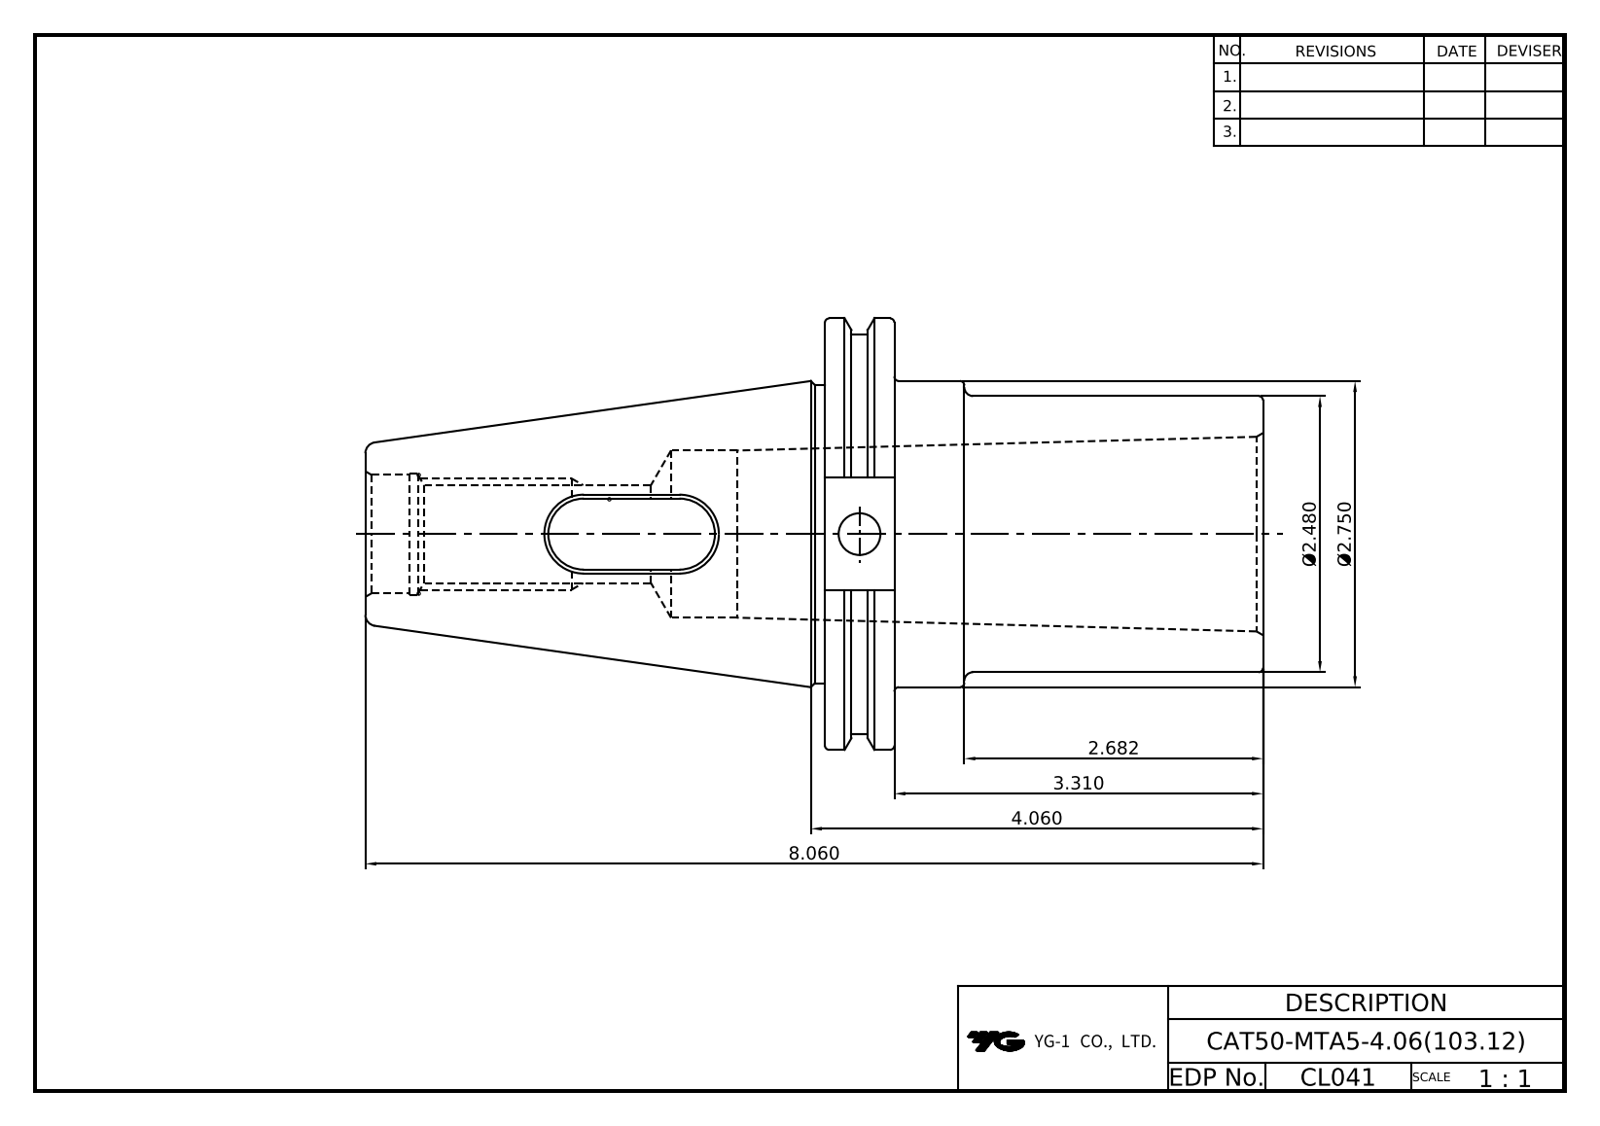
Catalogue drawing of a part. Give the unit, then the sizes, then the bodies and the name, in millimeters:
Units: millimetres
Overall size (bounding box): 204.72 × 98.42 × 94.69
Round holes (diameter × count): ⌀9.53 ×1, ⌀21.97 ×1, ⌀26.2 ×1, ⌀38.2 ×1
Round bosses / shafts (diameter × count): ⌀98.42 ×1, ⌀91.29 ×1, ⌀69.85 ×1, ⌀69.25 ×1, ⌀63 ×1
Partial cylindrical surfaces — rounded edges, fillets, slot ends (radius × count): R7.95 ×2
Main face-to-face distances: 15.88, 99.95, 84.07, 15.9, 5, 20.9, 104.77, 120.65, 204.72, 69.72
Volume: 416 015 mm³ · Surface area: 74 026 mm²
Bodies: 1 solid, 88 faces (35 planar, 17 cylindrical, 36 other)
Part name (STEP PRODUCT): LO-CAT50-MTA5-103.12
STEP written by: Autodesk Inventor 2025 (AUTOMOTIVE_DESIGN)
